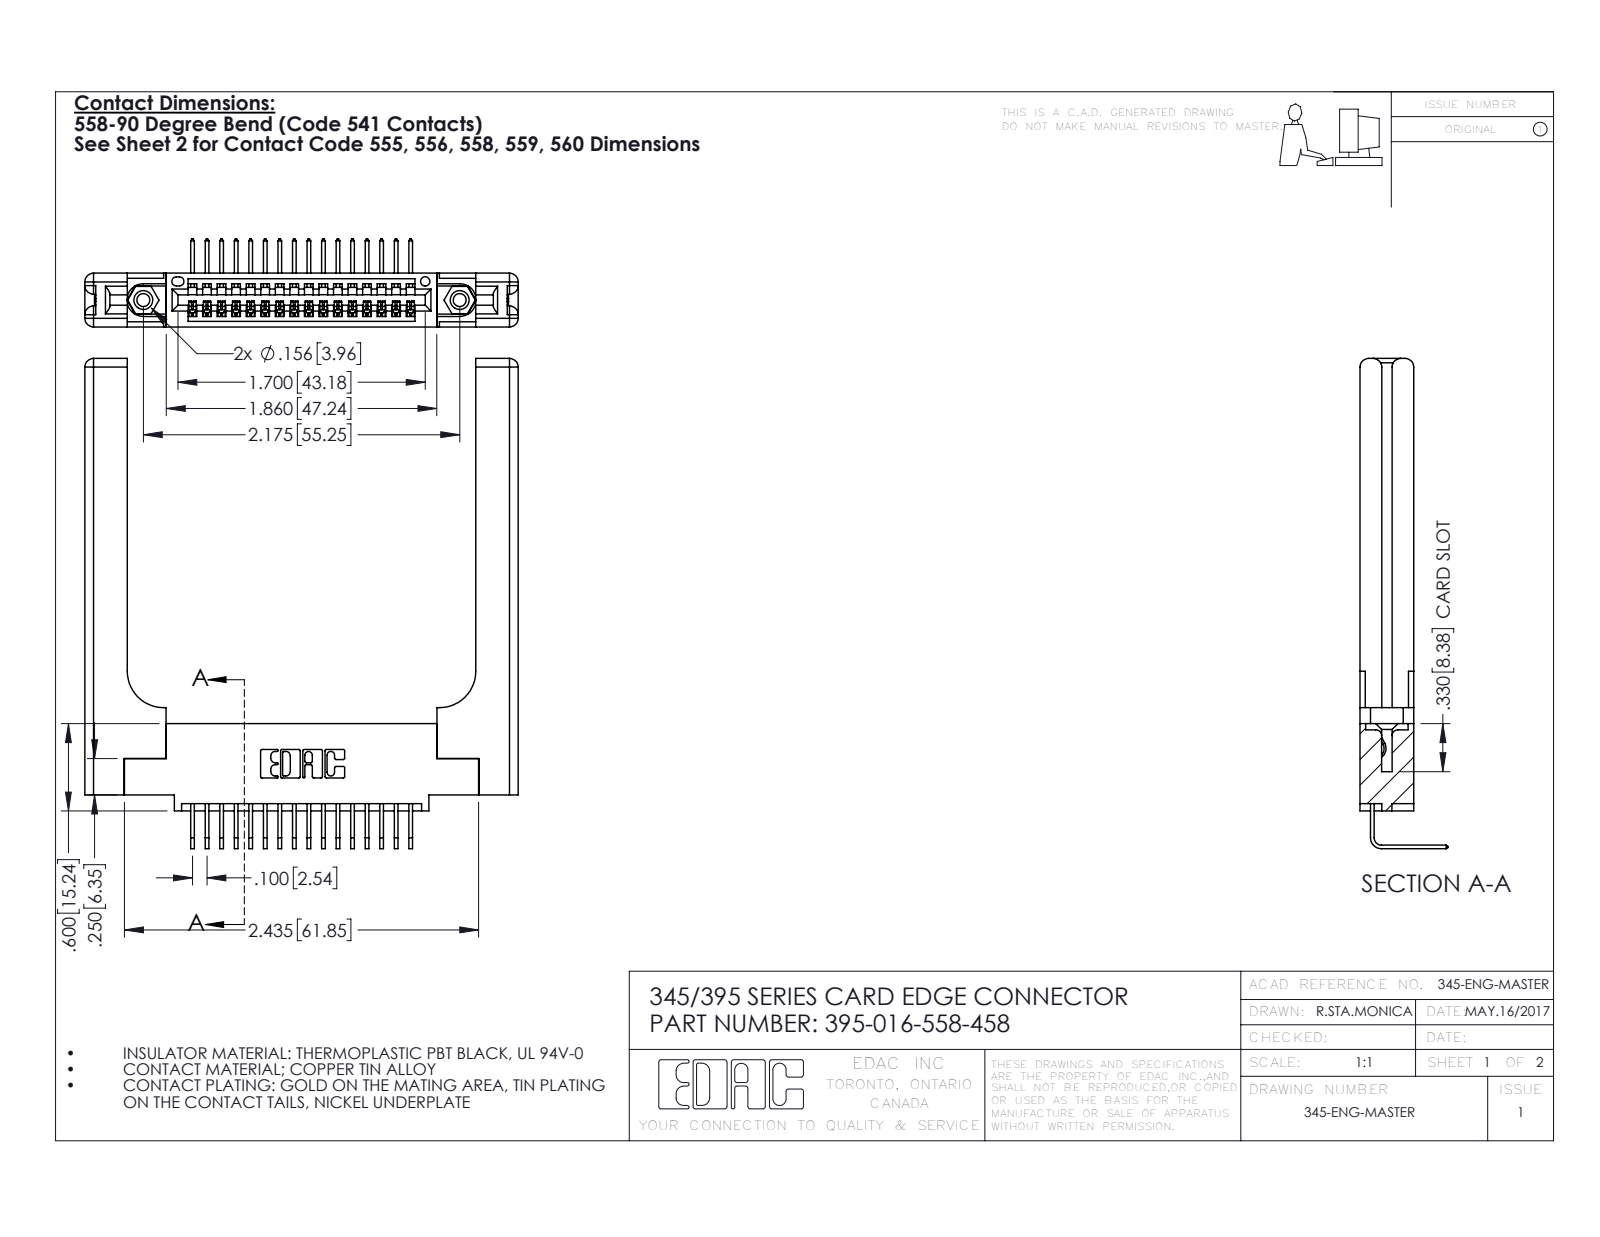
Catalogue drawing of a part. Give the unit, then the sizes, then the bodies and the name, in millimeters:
Units: millimetres
Overall size (bounding box): 85.6 × 75.7 × 15.4
Round holes (diameter × count): ⌀2.3 ×2, ⌀3.2 ×2, ⌀4 ×2, ⌀1.6 ×1
Round bosses / shafts (diameter × count): ⌀3.9 ×2
Partial cylindrical surfaces — rounded edges, fillets, slot ends (radius × count): R0.2 ×32, R0.3 ×22, R1.5 ×16, R0.2 ×6, R0.8 ×6, R0.7 ×3, R0.8 ×2, R0.8 ×2
Main face-to-face distances: 9.4, 1.8, 7.6, 3.8, 3.8, 2, 5.6, 2.5, 6.9, 0.6
Hole centre spacings: 6.9, 49.3, 55.2
Volume: 15 500 mm³ · Surface area: 14 590 mm²
Bodies: 21 solids, 1346 faces (904 planar, 382 cylindrical, 60 other)
Part name (STEP PRODUCT): 345-220-058_345-220-058; 395-016-558-458; 345-250-001_345-250-001-102; 345 Part_0.110 Offset - 0.156 Dia-TH (+1 more)
STEP written by: SolidWorks 2016 (CONFIG_CONTROL_DESIGN)
